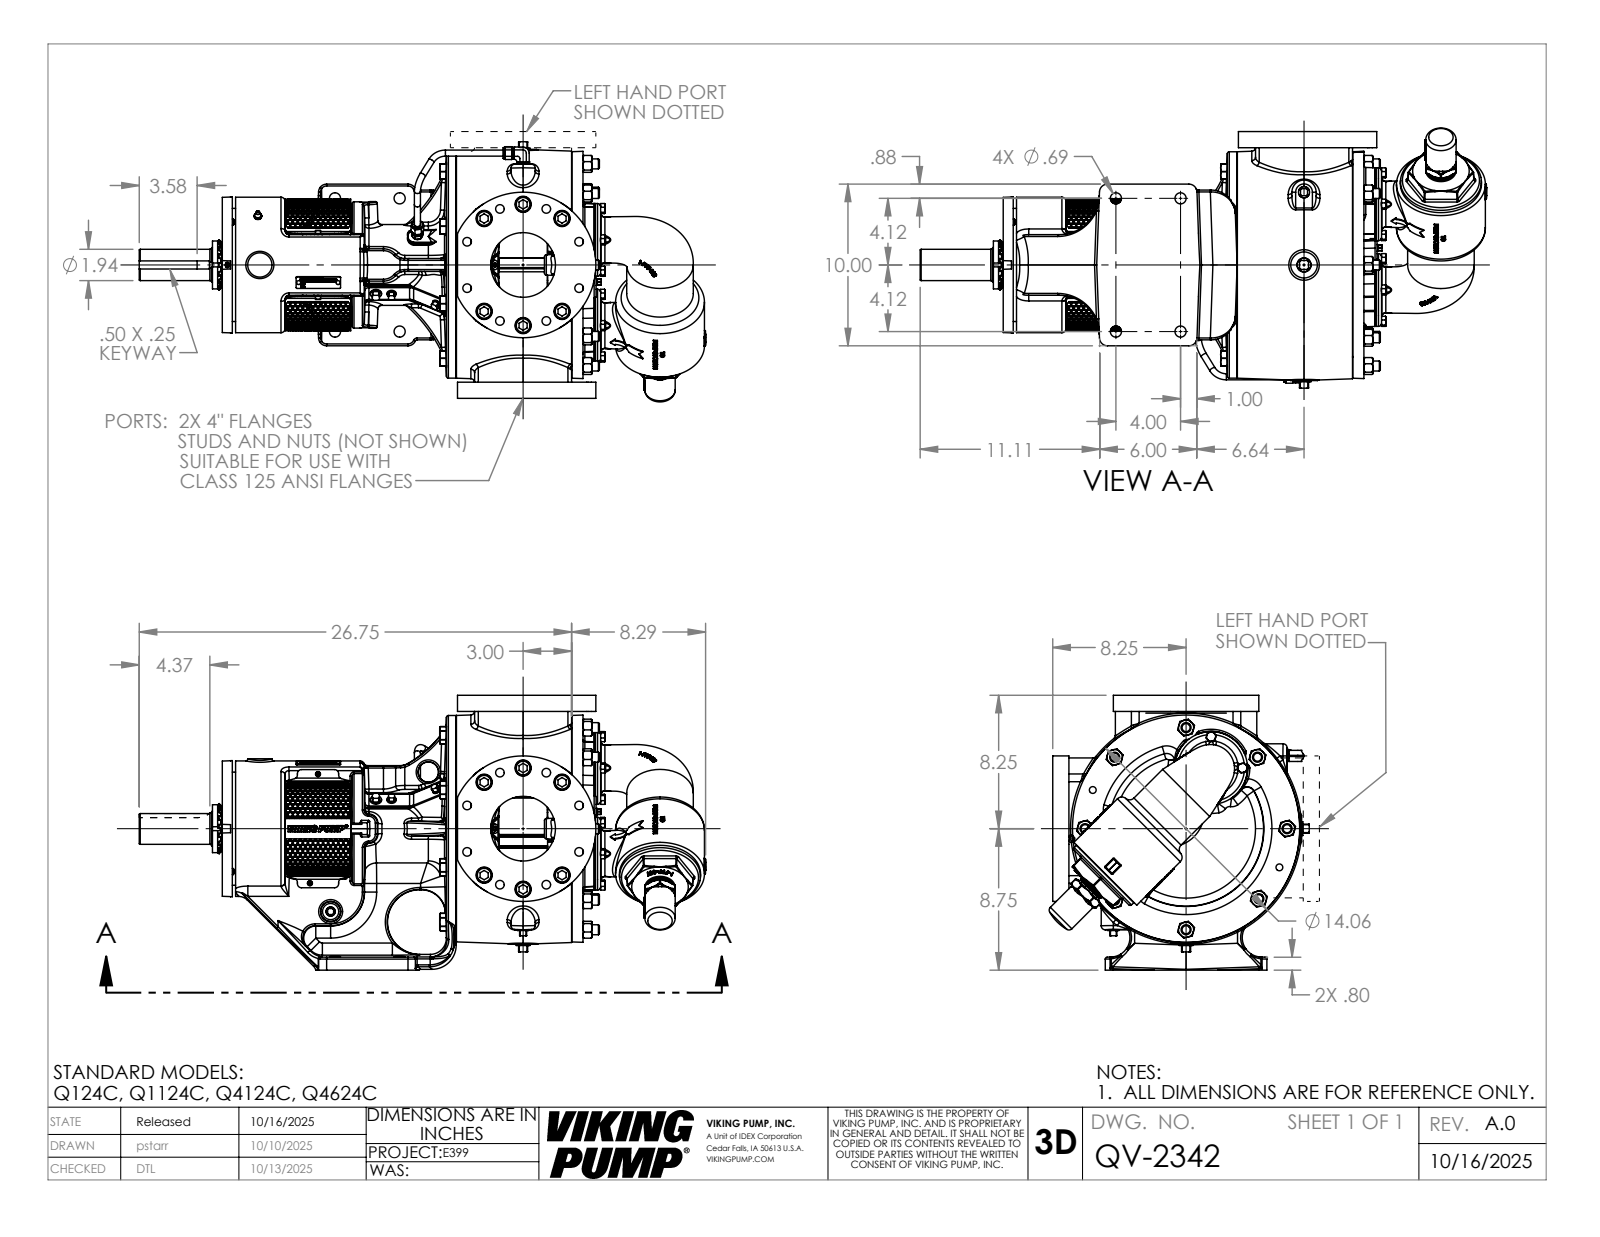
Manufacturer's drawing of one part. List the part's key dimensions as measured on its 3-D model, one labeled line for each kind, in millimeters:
Part name (STEP PRODUCT): QV-2342
STEP written by: SolidWorks 2024 (AUTOMOTIVE_DESIGN)
Units: millimetres
Bodies: 1 solid, 4913 faces (1677 planar, 860 cylindrical, 2376 other)
Overall size (bounding box): 890.1 × 431.8 × 411.3
Volume: 37 100 000 mm³ · Surface area: 1 521 000 mm²
Round holes (diameter × count): ⌀13.5 ×16, ⌀16.7 ×12, ⌀25.4 ×12, ⌀6.4 ×9, ⌀6.8 ×8, ⌀10.3 ×8, ⌀10.4 ×8, ⌀29.4 ×8, ⌀17.5 ×4, ⌀4 ×2, ⌀8 ×2, ⌀10.7 ×2
Round bosses / shafts (diameter × count): ⌀23.8 ×12, ⌀9.5 ×10, ⌀15.9 ×9, ⌀15.7 ×8, ⌀9.5 ×4, ⌀15.9 ×3, ⌀7.9 ×3, ⌀4.8 ×3
Partial cylindrical surfaces — rounded edges, fillets, slot ends (radius × count): R3 ×66, R6.4 ×22, R1.5 ×20, R0.4 ×18, R2.3 ×18, R1.8 ×16, R19.1 ×16, R0.8 ×13
Main face-to-face distances: 431.8, 566.9, 97, 469.8, 25.4, 202.5, 105.5, 364.4, 3, 22.4
Hole centre spacings: 95.3, 134.7, 72.9, 176, 190.5, 52.8, 37.2, 79.6
